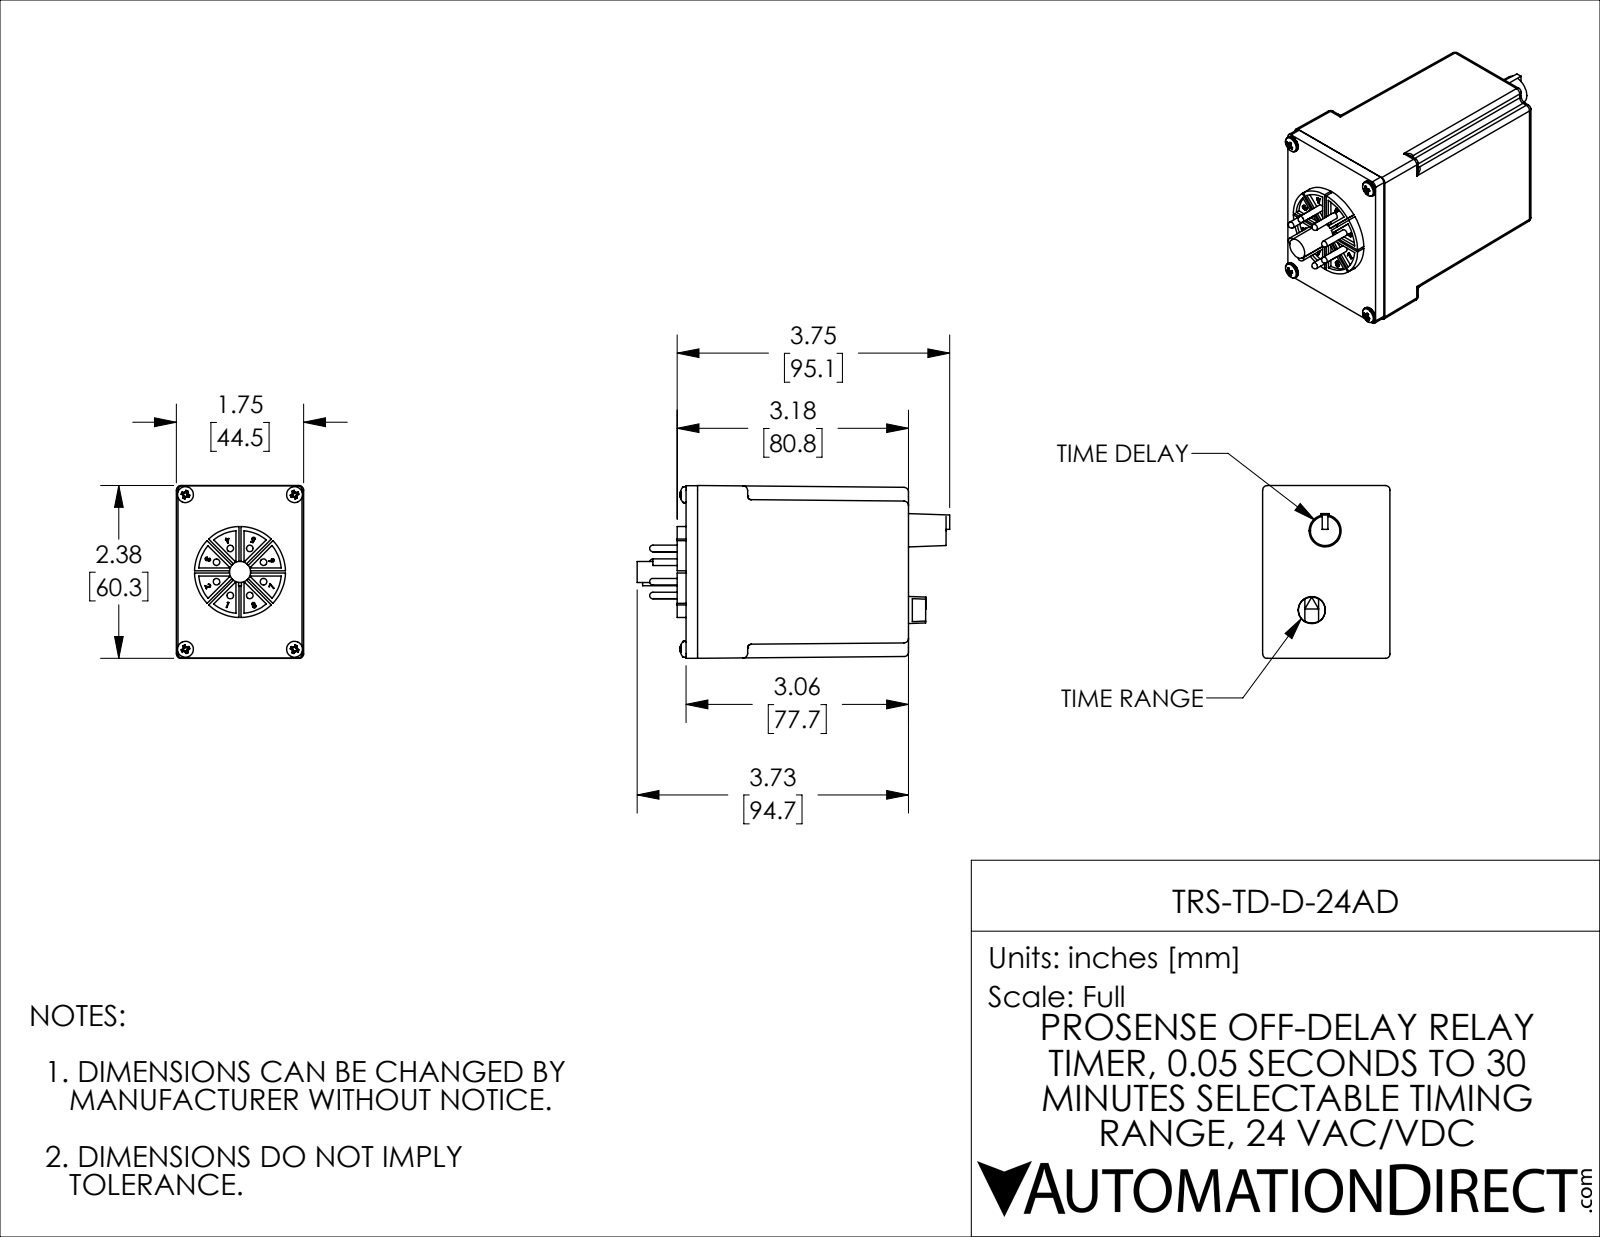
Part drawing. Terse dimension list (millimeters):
name: TRS-TD-D-24AD
written by: SolidWorks 2021 (CONFIG_CONTROL_DESIGN)
unit: mm
bodies: 17 solids, 554 faces (232 planar, 164 cylindrical, 158 other)
size: 109.1 × 60.3 × 44.5
volume: 202 100 mm³; area: 29 670 mm²
holes: 4× ⌀3.2
bosses: 8× ⌀2.3, 4× ⌀5.6, 1× ⌀31.8, 1× ⌀7.4
rounds: 32× R1.6, 8× R0.1, 4× R1.3, 1× R14.5
face distances: 73.7, 4.1, 77.7, 1.8, 5.8, 79.5, 4.8, 3, 1.3, 7.1
hole spacings: 38.1, 54, 66.1
